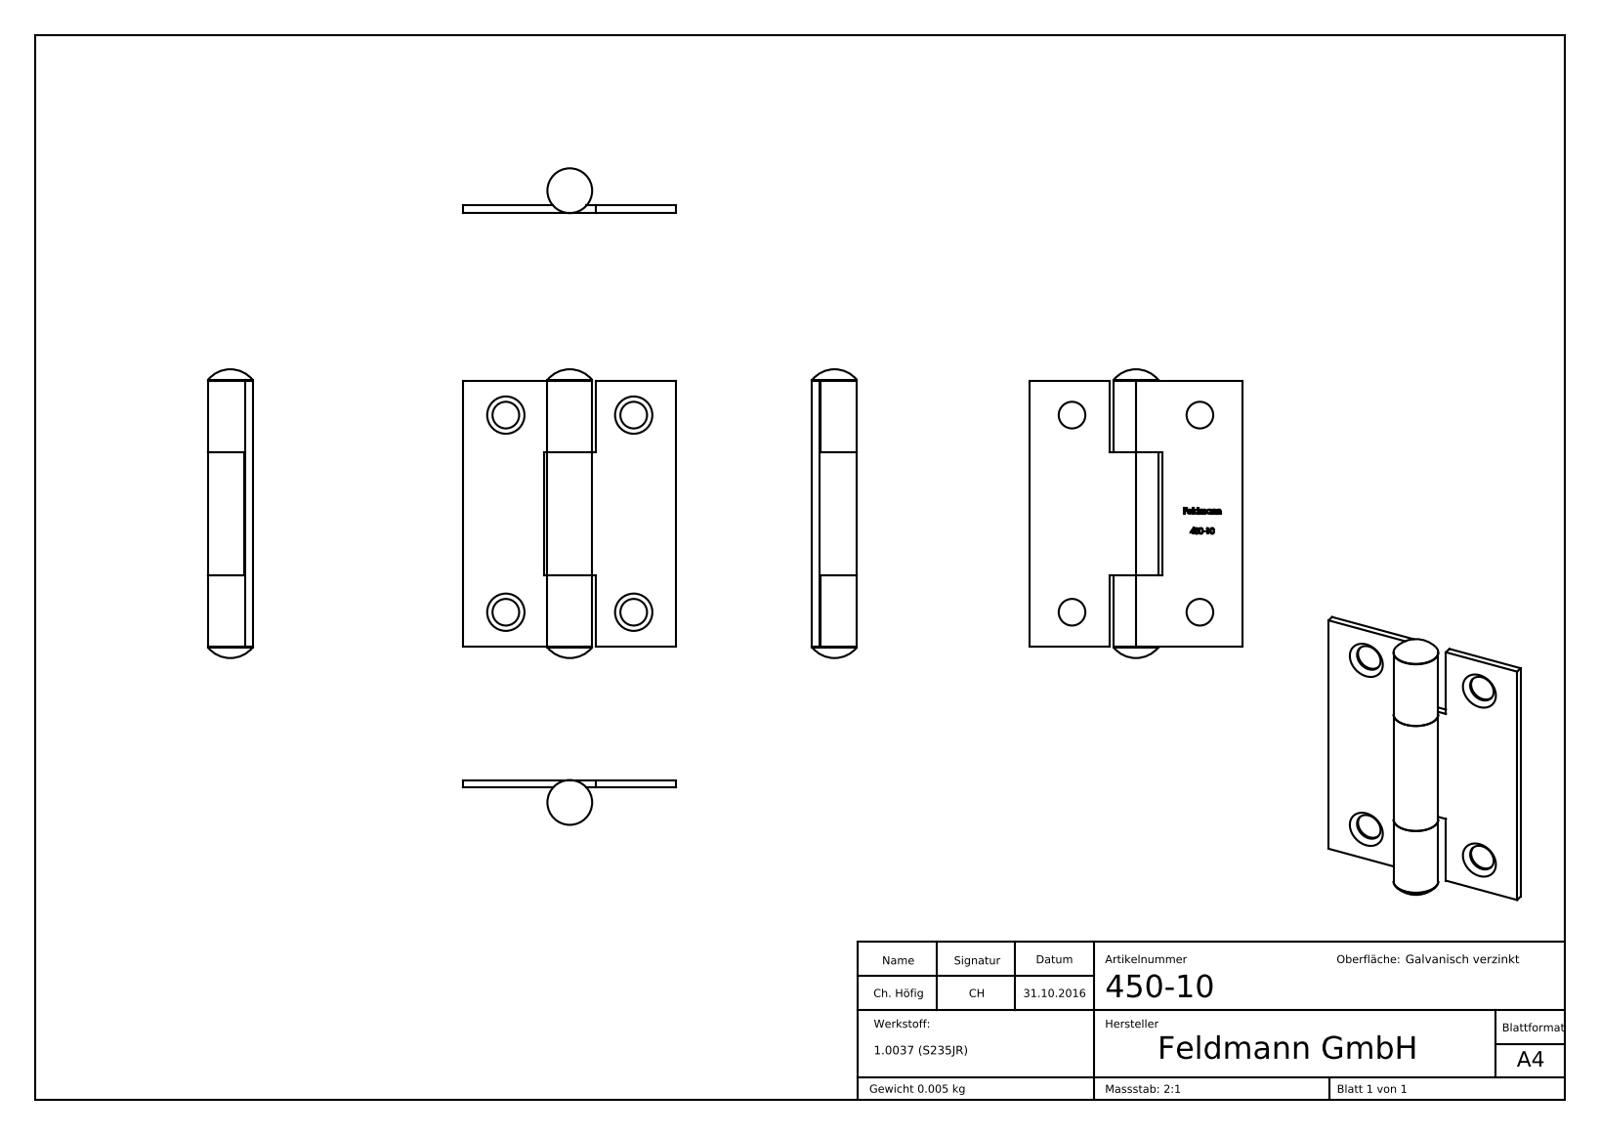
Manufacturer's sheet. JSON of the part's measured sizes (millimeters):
{"part_name": "450-10 Teil1; 450-10 Teil3; 450-10; 450-10 Teil2", "step_written_by": "SolidWorks 2018 (CONFIG_CONTROL_DESIGN)", "units": "millimeters", "bodies": {"solids": 3, "faces": 216, "planar": 125, "cylindrical": 11, "other": 80}, "overall_size": [27.1, 20, 4.2], "volume_mm3": 623, "surface_area_mm2": 1737, "round_holes": [[2.5, 4], [2.8, 1]], "round_bosses_or_shafts": [[4.2, 1]], "face_to_face_distances": [0.7, 6.75, 18.25, 25, 20, 7.55, 12.45, 11.5, 6.8, 18.3], "hole_center_spacings": [12, 18.5, 22.05]}
